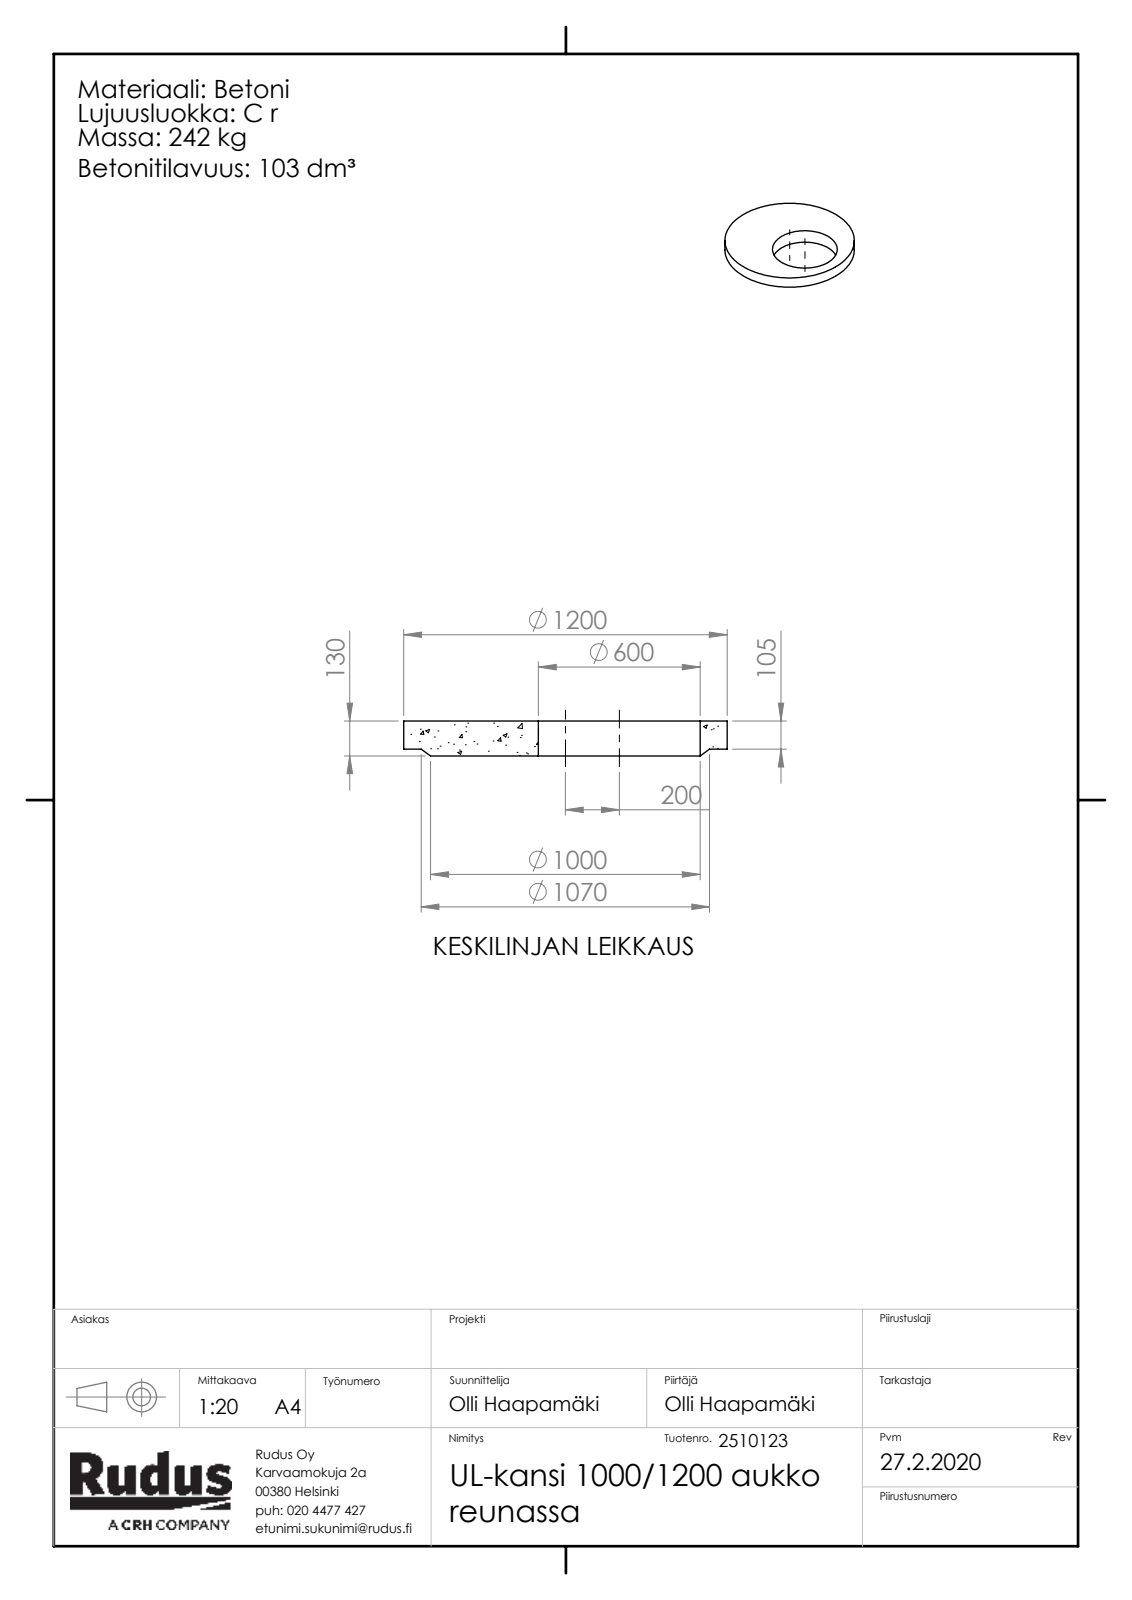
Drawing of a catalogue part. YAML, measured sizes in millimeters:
part_name: "Rudus 2510123 UL-kansi 1000_1200 aukko reunassa; UL-osa-kansi_aukko"
step_written_by: "SolidWorks 2019 (CONFIG_CONTROL_DESIGN)"
units: millimeters
bodies: {solids: 1, faces: 9, planar: 3, cylindrical: 4, other: 2}
overall_size: [1200, 1200, 130]
volume: 103000000
surface_area: 2363000
round_holes:
  - {diameter: 600, count: 1}
round_bosses_or_shafts:
  - {diameter: 1200, count: 1}
face_to_face_distances: [130, 25, 105]
